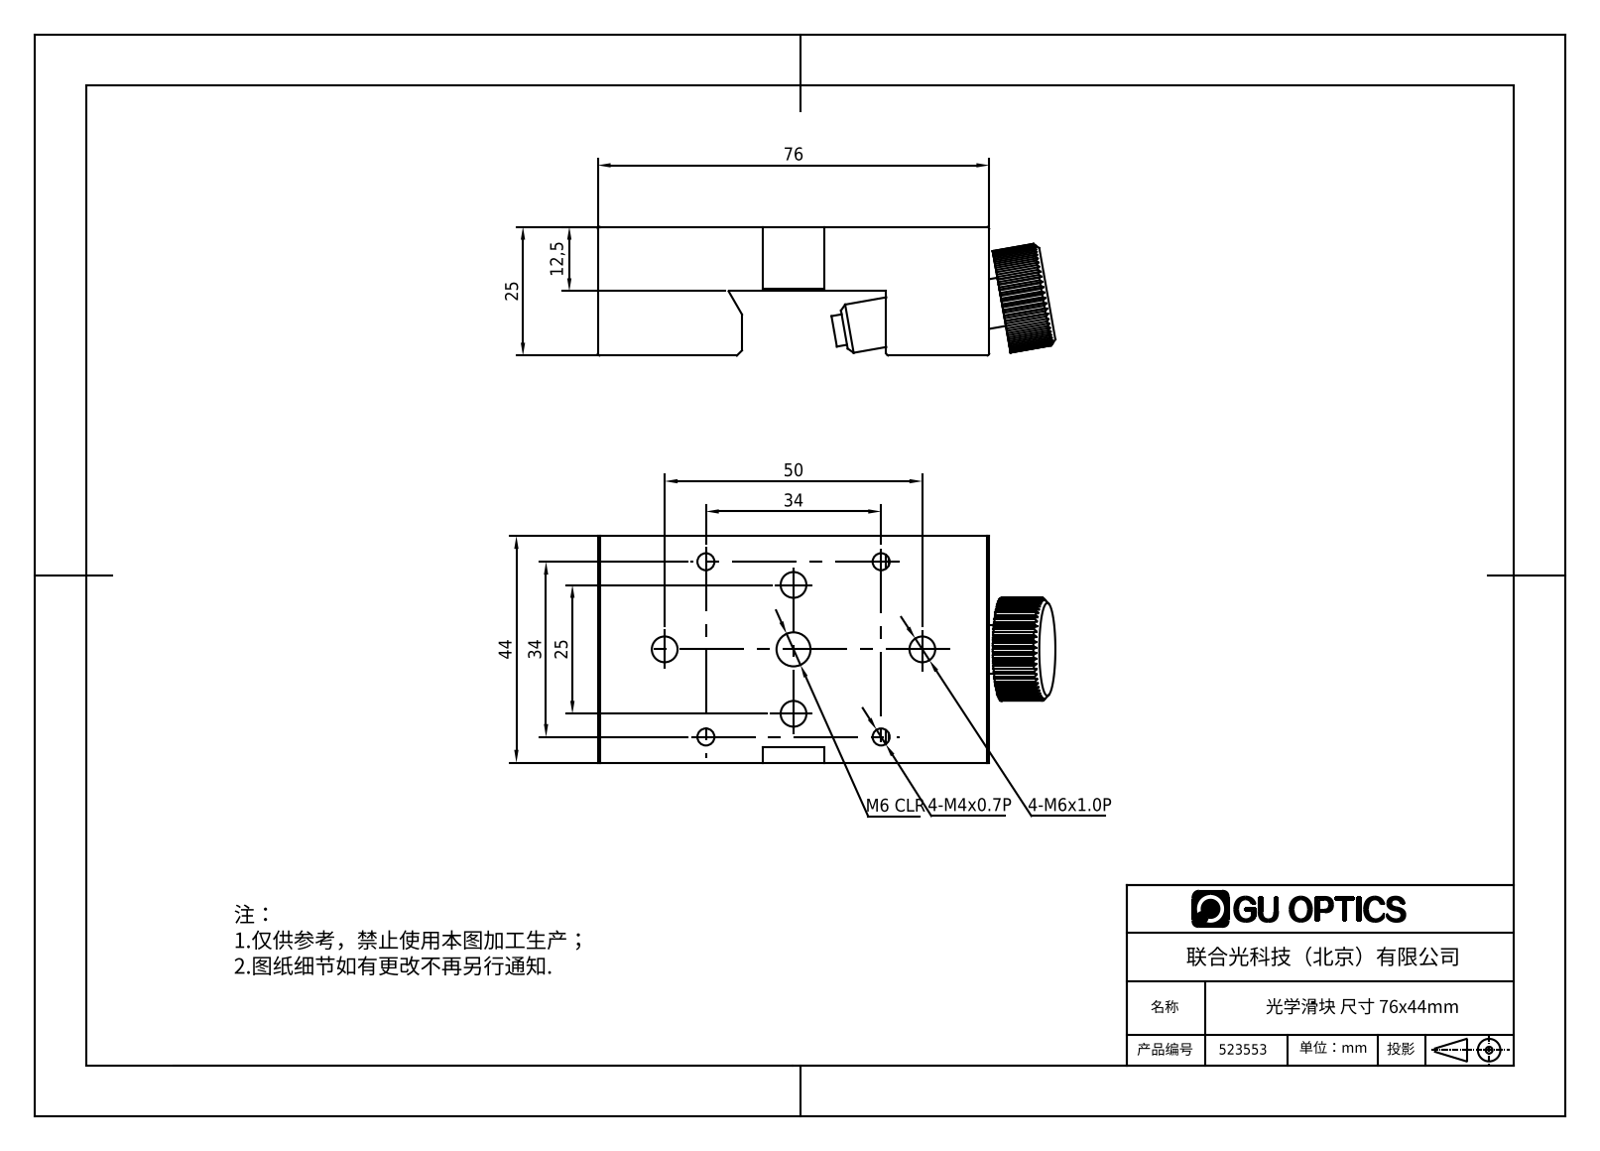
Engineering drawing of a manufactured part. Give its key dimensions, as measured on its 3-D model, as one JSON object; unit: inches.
{"part_name": "CR-2", "step_written_by": "SolidWorks 2012 (CONFIG_CONTROL_DESIGN)", "units": "inches", "bodies": {"solids": 0, "faces": 210, "planar": 133, "cylindrical": 75, "other": 2}, "overall_size": [3.497, 1.732, 0.984], "round_holes": [[0.13, 4], [0.197, 4], [0.256, 1], [0.26, 1], [0.433, 1]], "round_bosses_or_shafts": [[0.374, 1], [0.236, 1]], "partial_cylinders_radius": [[0.02, 5], [0.394, 1]], "face_to_face_distances": [0.492, 0.984, 1.732, 2.992, 1.102, 2.205, 0.787, 1.89, 0.354, 0.374], "hole_center_spacings": [0.693, 0.74, 0.946, 1.1, 1.339, 1.341, 1.784, 0.984]}
